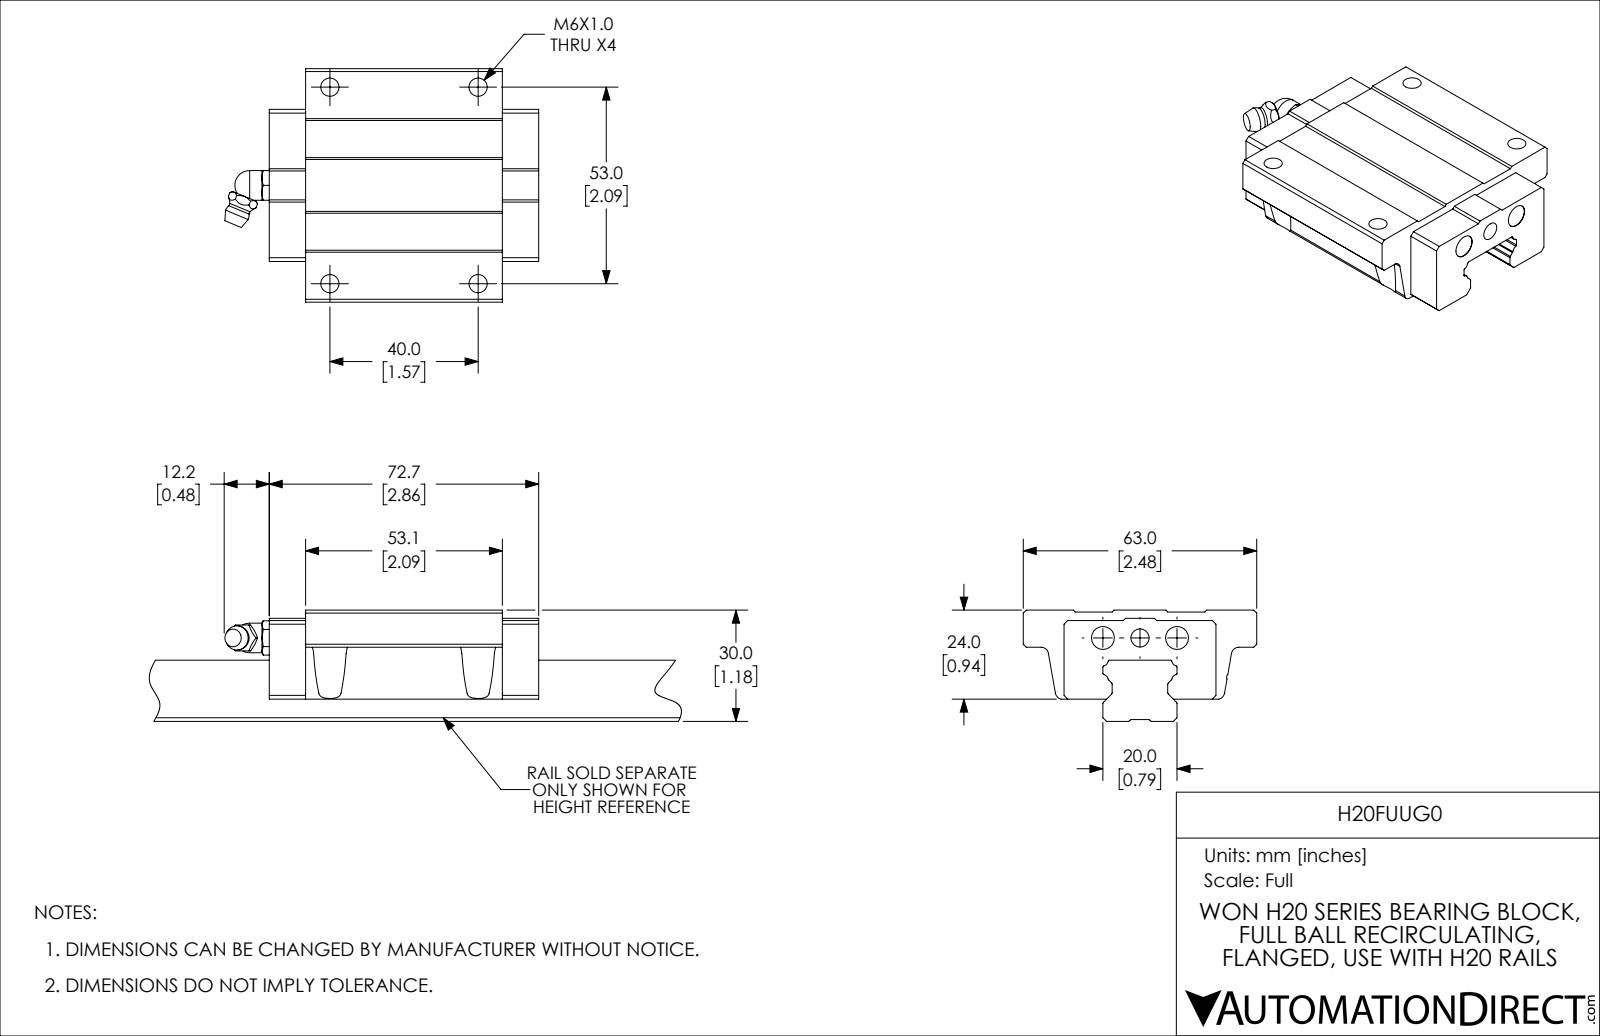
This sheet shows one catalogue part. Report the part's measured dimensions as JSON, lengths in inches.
{"part_name": "H20FUUG0", "step_written_by": "SolidWorks 2019 (CONFIG_CONTROL_DESIGN)", "units": "inches", "bodies": {"solids": 2, "faces": 161, "planar": 85, "cylindrical": 57, "other": 19}, "overall_size": [3.335, 2.48, 0.945], "volume_in3": 4.351, "surface_area_in2": 25.8, "round_holes": [[0.194, 5], [0.244, 2]], "round_bosses_or_shafts": [[0.315, 1], [0.236, 1]], "partial_cylinders_radius": [[0.02, 8], [0.012, 4], [0.063, 4], [0.079, 4], [0.187, 4], [0.039, 1]], "face_to_face_distances": [0.945, 0.413, 0.512, 0.531, 0.925, 0.02, 0.386, 2.476, 0.433, 2.047], "hole_center_spacings": [0.394, 1.575, 2.087, 2.614, 0.787]}
